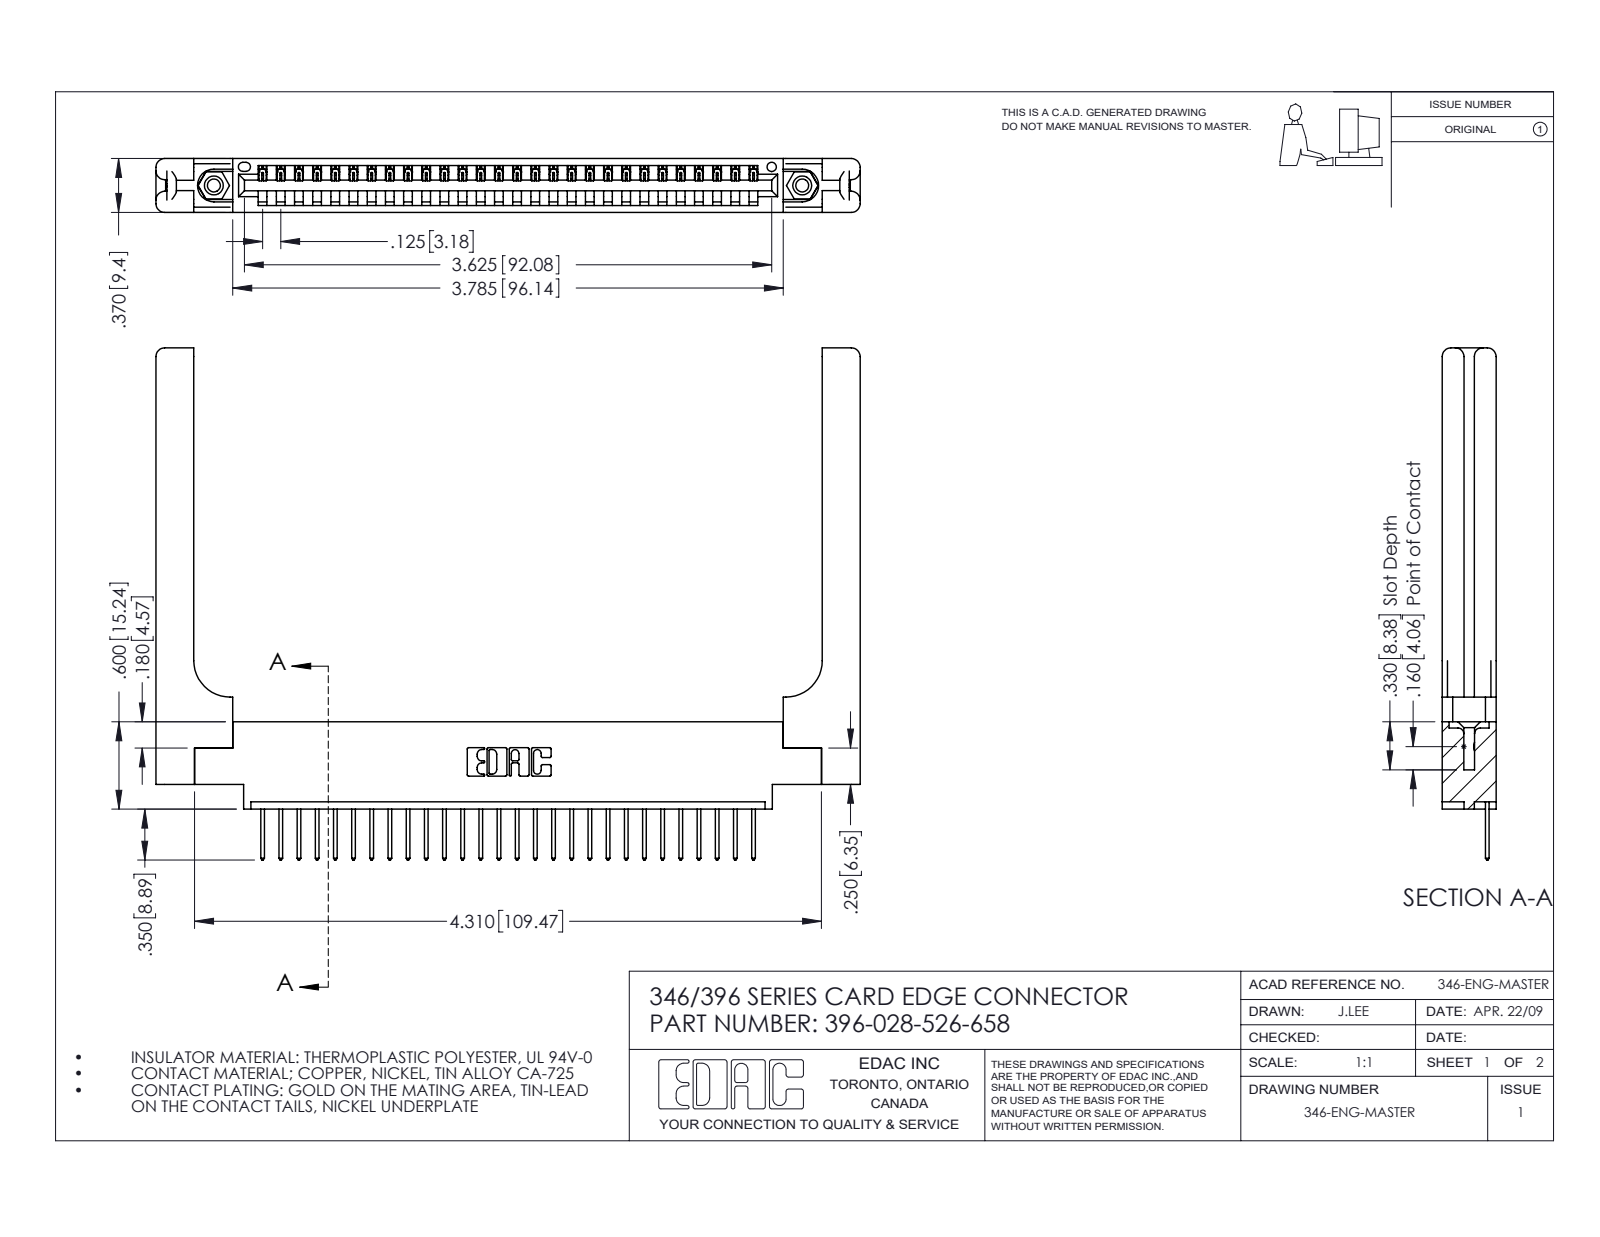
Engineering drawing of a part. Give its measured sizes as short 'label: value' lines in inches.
name: 345-250-001_345-250-001-102; 396-028-526-658; 345-292-001_345-293-126; 346-220-058_345-220-058 (+1 more)
written by: SolidWorks 2016 (CONFIG_CONTROL_DESIGN)
unit: in
bodies: 33 solids, 2006 faces (1348 planar, 598 cylindrical, 60 other)
size: 4.841 × 3.52 × 0.37
volume: 1.16 in³; area: 30.26 in²
holes: 2× ⌀0.089, 2× ⌀0.125, 2× ⌀0.156, 1× ⌀0.064
bosses: 2× ⌀0.155
rounds: 56× R0.006, 56× R0.01, 22× R0.01, 16× R0.06, 6× R0.007, 6× R0.031, 3× R0.026, 2× R0.03
face distances: 0.37, 0.072, 0.048, 0.322, 0.148, 0.15, 0.25, 0.298, 0.025, 0.076
hole spacings: 0.246, 3.837, 4.045
